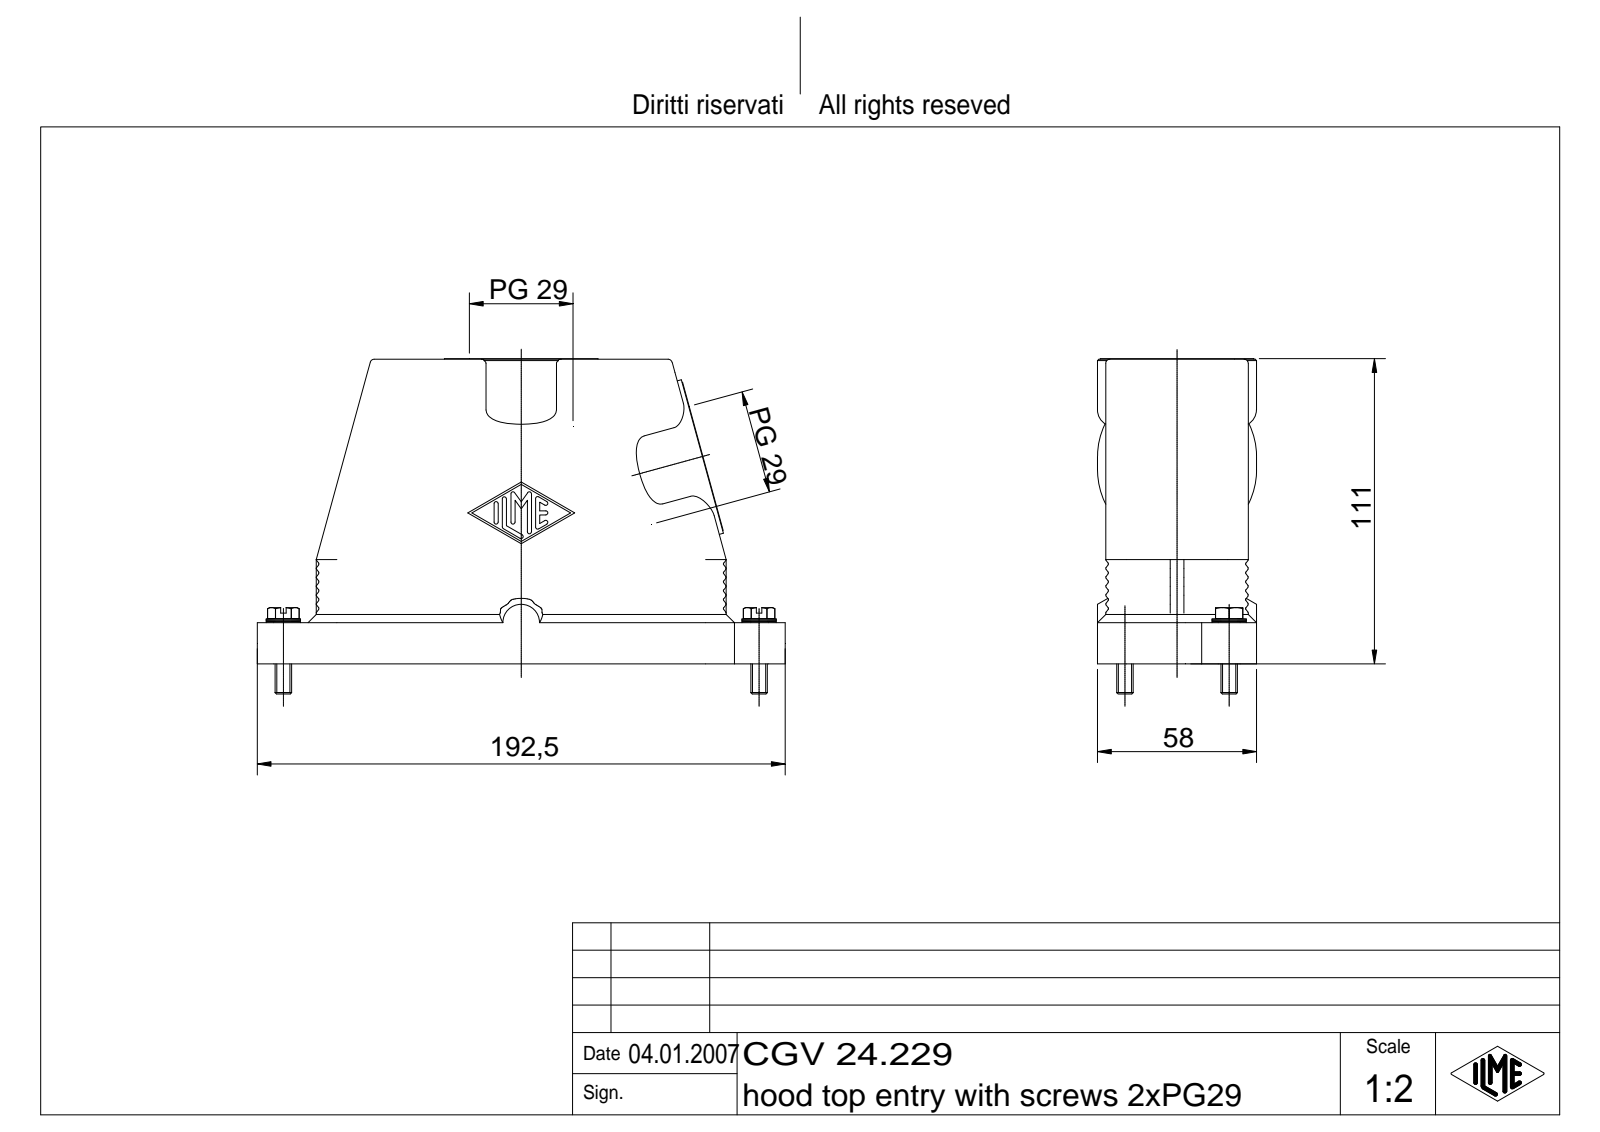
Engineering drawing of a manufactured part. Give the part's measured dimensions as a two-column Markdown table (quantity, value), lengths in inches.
| quantity | value |
| --- | --- |
| part name | CGV 24.229 |
| STEP written by | Autodesk Inventor 7 (AUTOMOTIVE_DESIGN) |
| units | inches |
| bodies | 3 solids, 769 faces (189 planar, 197 cylindrical, 383 other) |
| overall size | 7.579 × 4.811 × 2.283 |
| volume | 13.88 in³ |
| surface area | 167.7 in² |
| round holes (diameter × count) | 0.097 × 2, 0.126 × 2, 0.26 × 2, 0.591 × 2, 1.397 × 2 |
| round bosses / shafts (diameter × count) | 2.283 × 2, 2.205 × 2, 0.492 × 2, 0.236 × 2 |
| partial cylindrical surfaces (radius × count) | 0.02 × 39, 0.03 × 14, 0.295 × 8, 0.236 × 6, 0.059 × 4, 0.118 × 4, 0.226 × 2, 0.413 × 2 |
| main face-to-face distances | 0.118, 2.047, 1.929, 1.811, 0.236, 2.165, 0.098, 0.02, 2.283, 0.138 |
| hole center spacings | 1.385, 2.115, 3.496, 5.611, 4.23, 6.993 |
